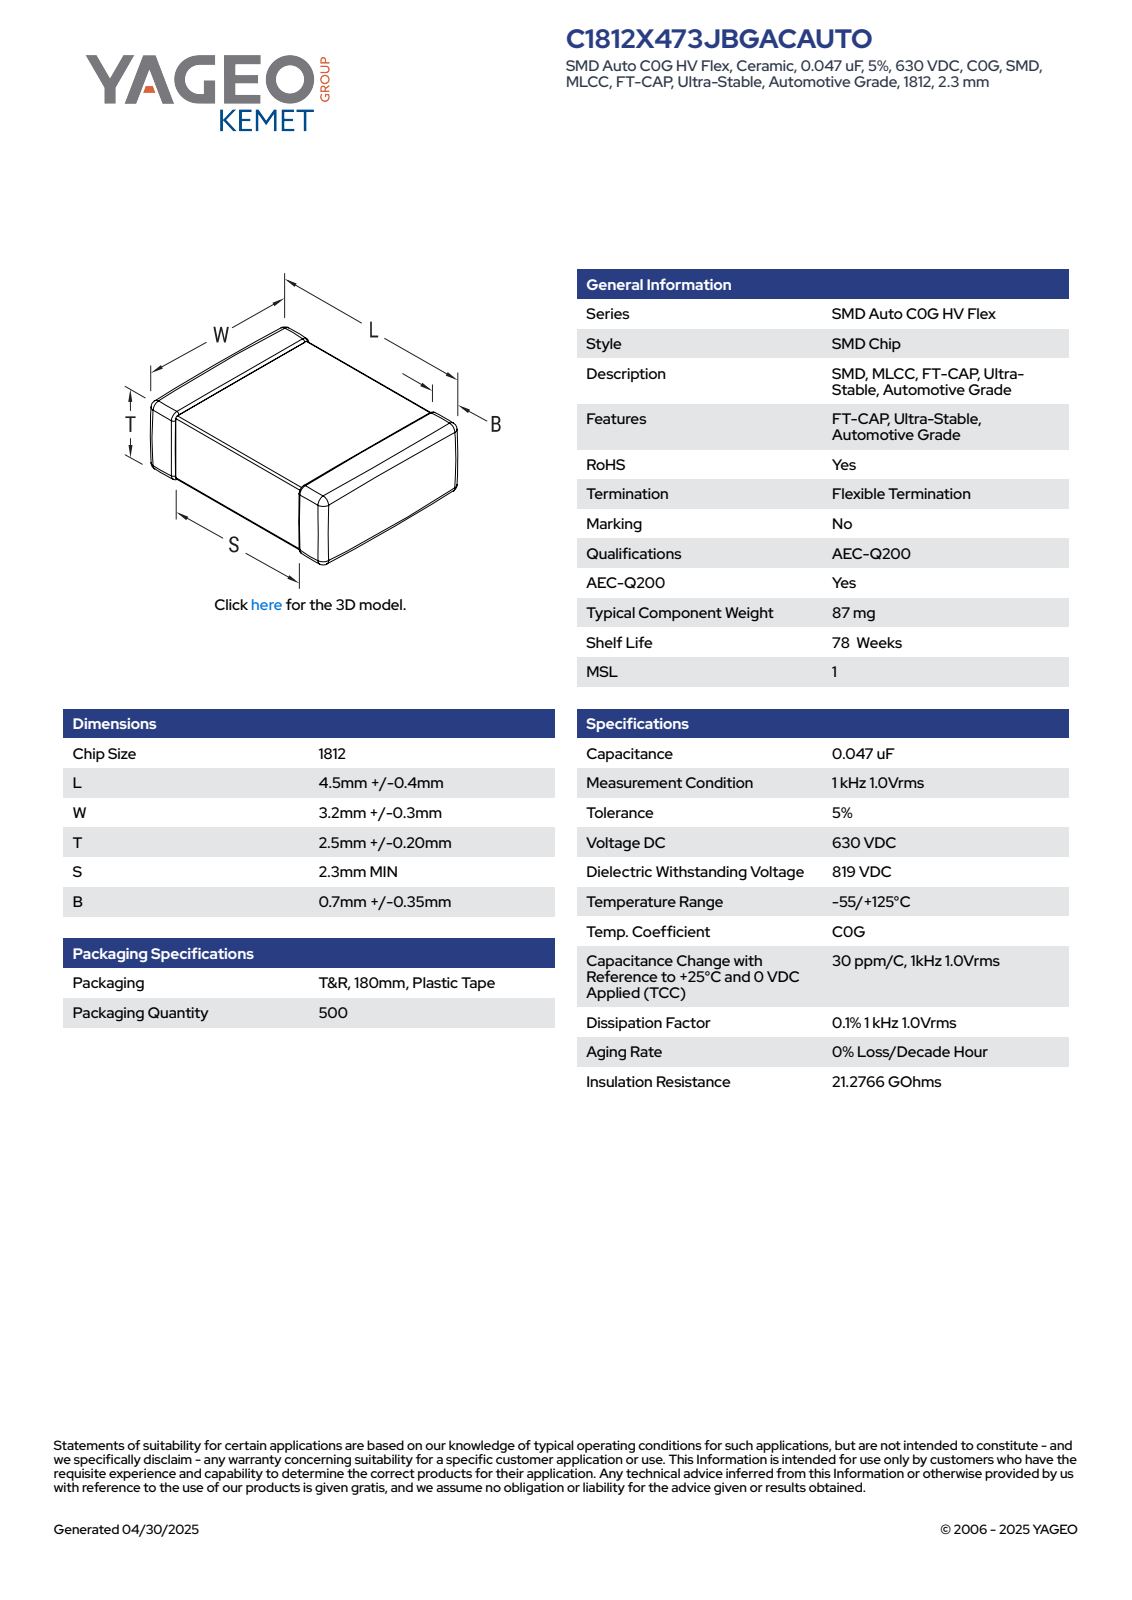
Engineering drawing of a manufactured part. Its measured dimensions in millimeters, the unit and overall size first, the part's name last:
Units: millimetres
Overall size (bounding box): 4.9 × 3.5 × 2.7
Main face-to-face distances: 2.63, 3.43, 2.56, 4.9, 3.36, 2.7, 3.5, 0.52, 2.25, 2.13
Volume: 44 mm³ · Surface area: 79 mm²
Bodies: 4 solids, 121 faces (71 planar, 34 cylindrical, 16 other)
Part name (STEP PRODUCT): CCS_CCSTD_1812_L4.9W3.5T2.7B0.7
STEP written by: SolidWorks 2021 (AUTOMOTIVE_DESIGN)
